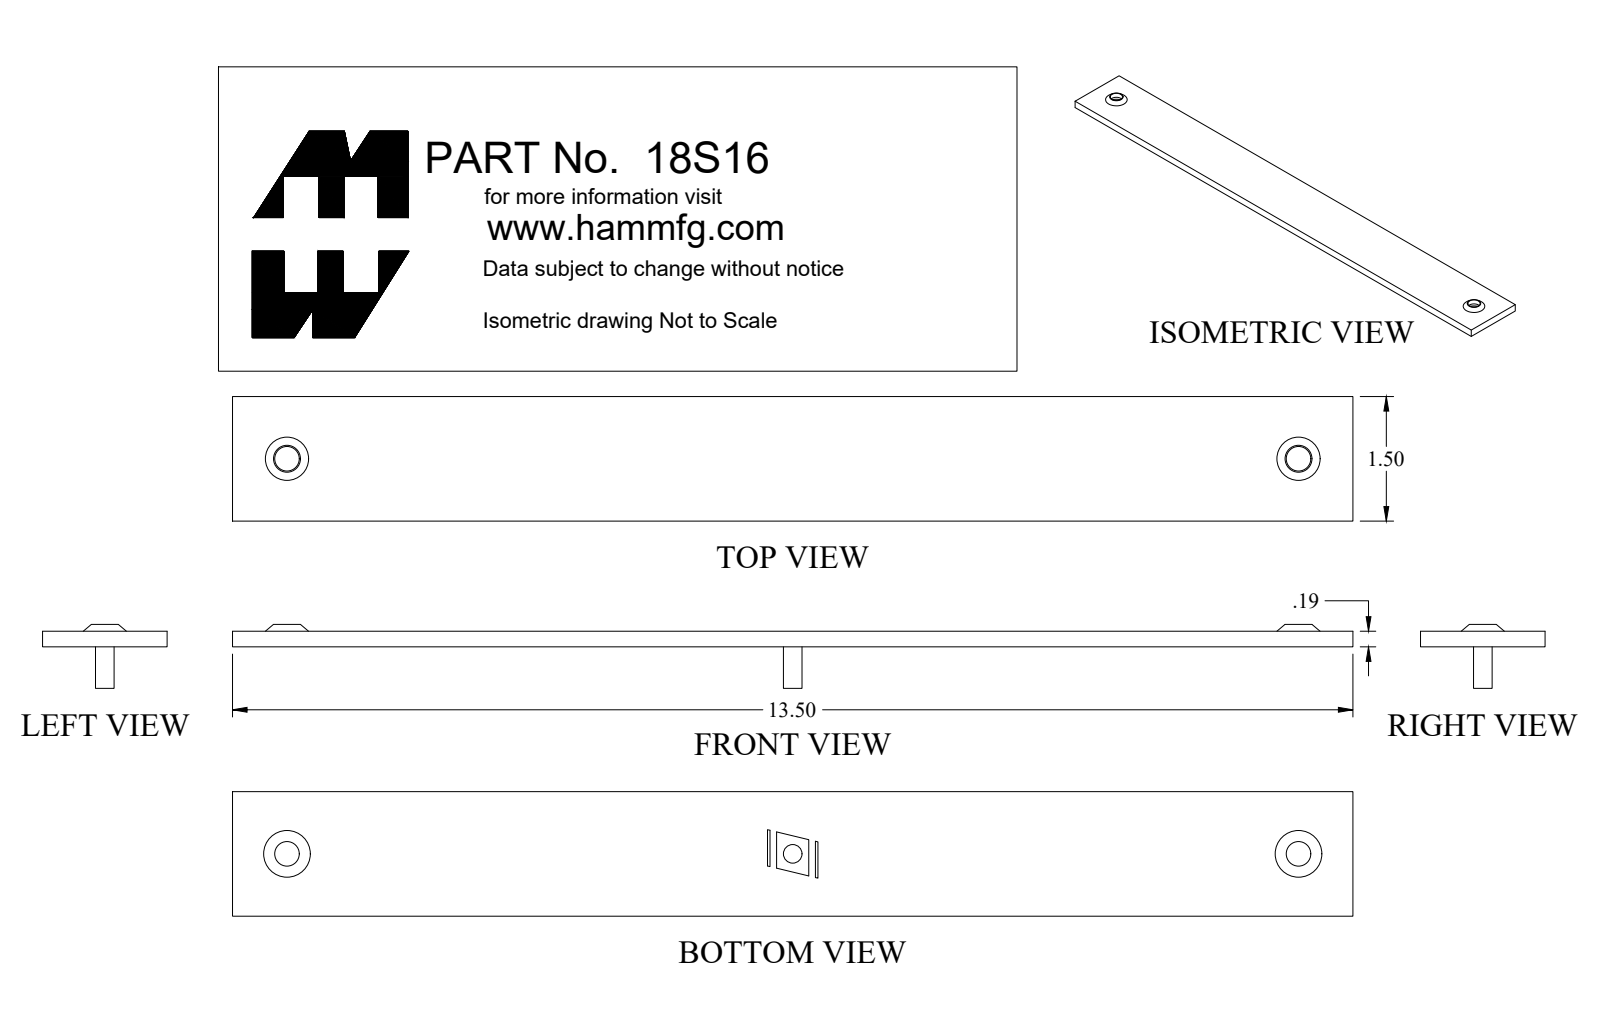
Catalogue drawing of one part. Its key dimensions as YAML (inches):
part_name: "18S16_Default"
step_written_by: "SolidWorks 2018 (CONFIG_CONTROL_DESIGN)"
units: inches
bodies: {solids: 1, faces: 20, planar: 8, cylindrical: 4, other: 8}
overall_size: [13.5, 1.5, 0.27]
volume: 3.769
surface_area: 46.35
round_holes:
  - {diameter: 0.296, count: 2}
face_to_face_distances: [0.188, 1.5, 13.5, 0.27, 0.082]
hole_center_spacings: [12.188]
